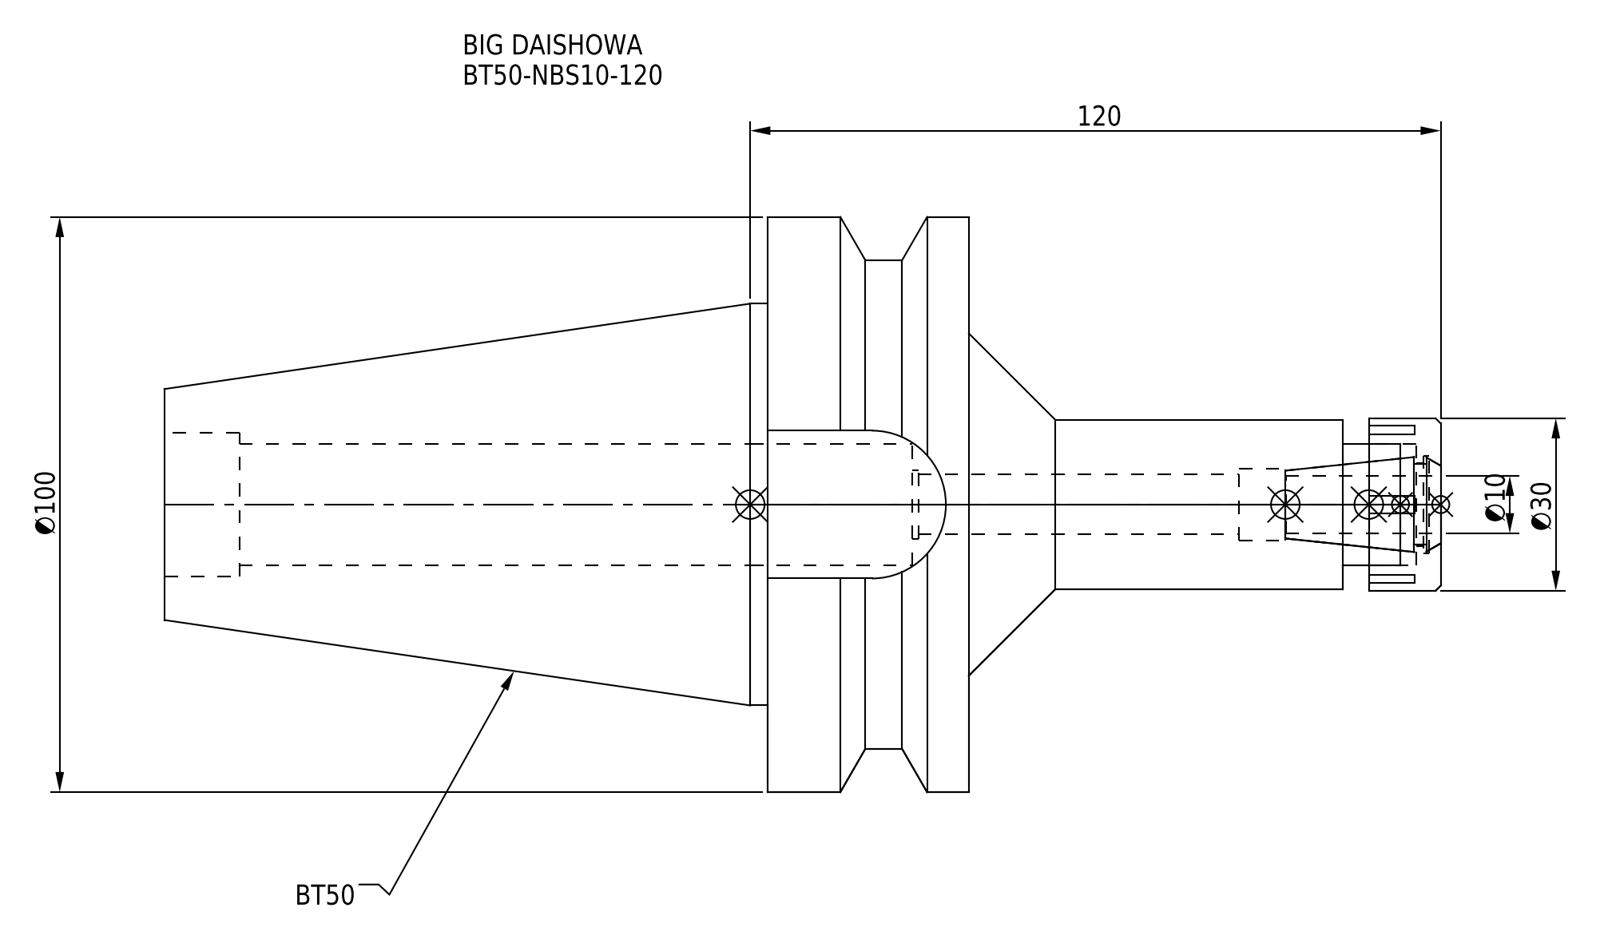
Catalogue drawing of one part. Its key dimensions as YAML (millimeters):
part_name: "BT50-NBS10-120; NBN10_1.stp; BT50-NBS10-120_1.stp; BT50NB10120-100_ASM.stp (+3 more)"
step_written_by: "SolidWorks 2019 (CONFIG_CONTROL_DESIGN)"
units: millimeters
bodies: {solids: 2, faces: 93, planar: 45, cylindrical: 34, other: 14}
overall_size: [221.8, 100, 100]
volume: 504203
surface_area: 66200
round_holes:
  - {diameter: 10.4, count: 1}
  - {diameter: 12, count: 1}
  - {diameter: 12.5, count: 1}
  - {diameter: 14.5, count: 1}
  - {diameter: 17, count: 1}
  - {diameter: 21, count: 1}
  - {diameter: 21.2, count: 1}
  - {diameter: 25, count: 1}
round_bosses_or_shafts:
  - {diameter: 100, count: 1}
  - {diameter: 85, count: 1}
  - {diameter: 69.85, count: 1}
  - {diameter: 30, count: 1}
  - {diameter: 29.5, count: 1}
partial_cylinders:
  - {radius: 12.85, count: 1}
face_to_face_distances: [35, 139.8, 104.8, 70.8, 117, 82, 221.8, 25.7, 91.8, 4.5]
